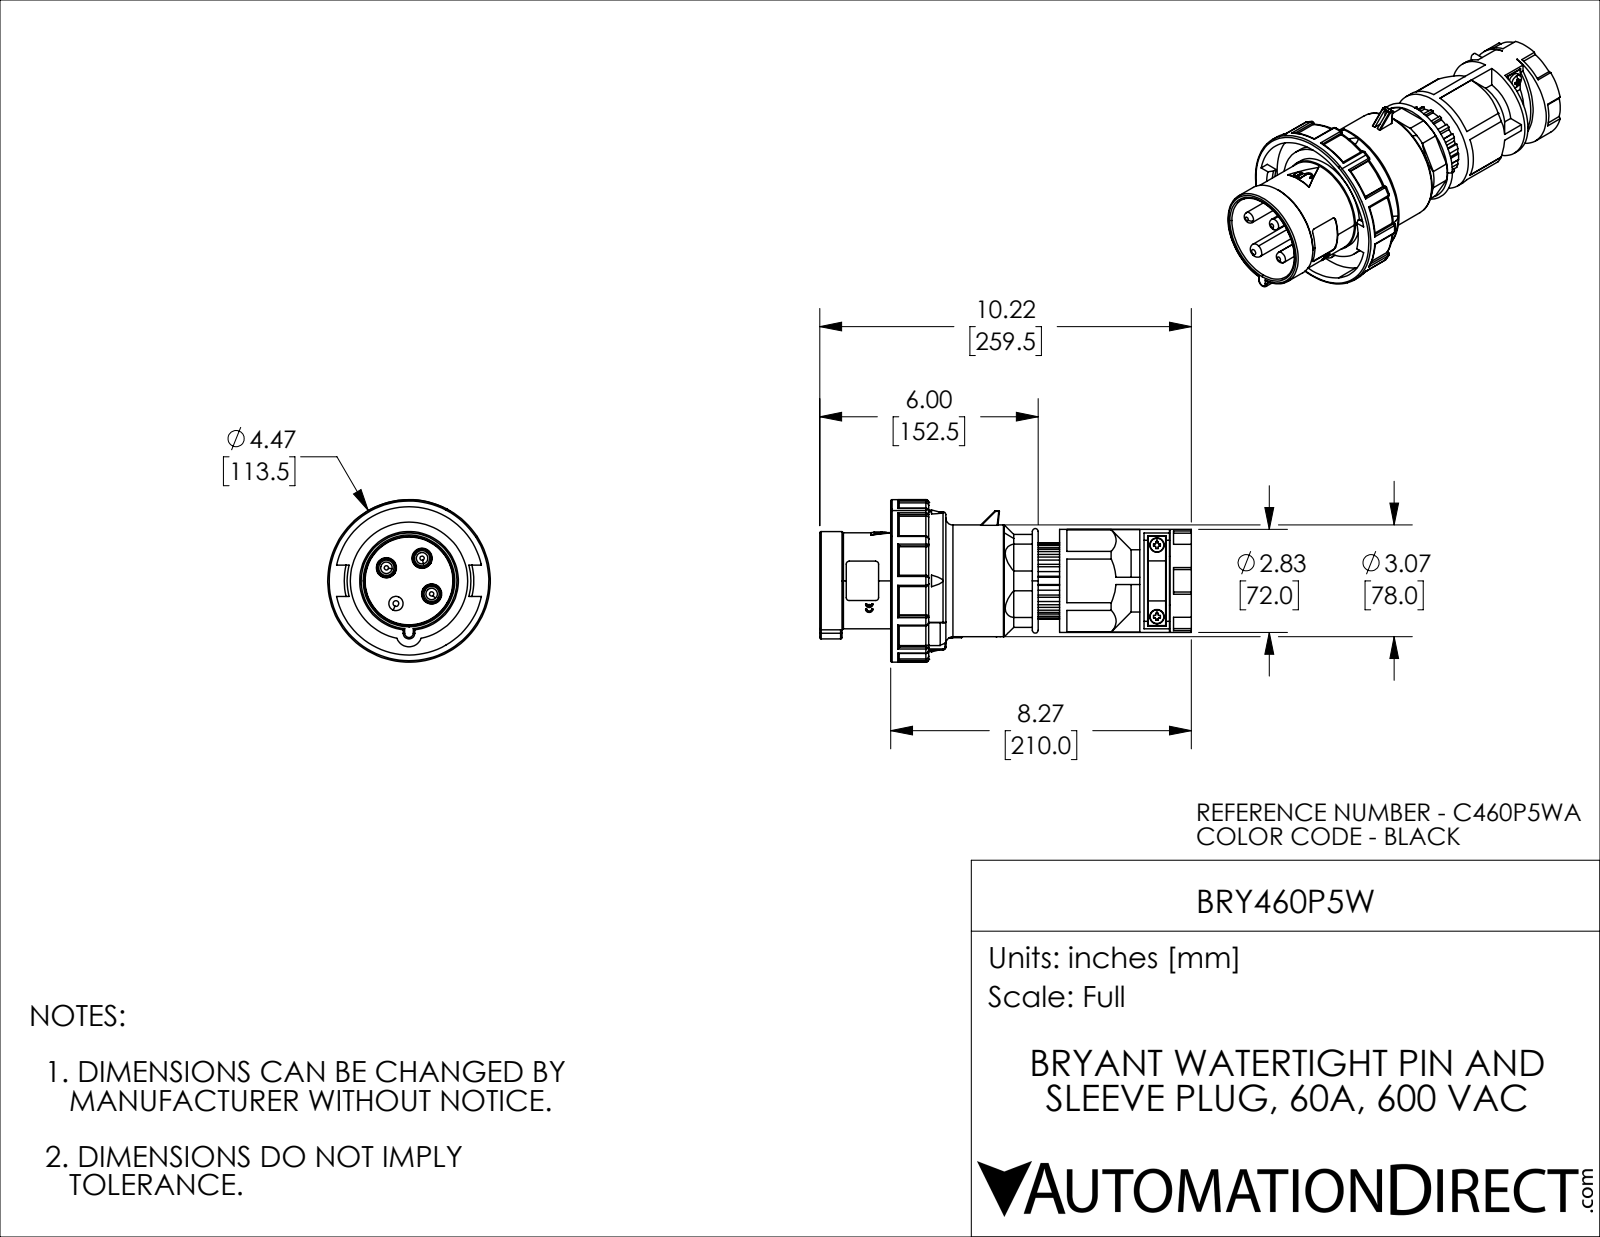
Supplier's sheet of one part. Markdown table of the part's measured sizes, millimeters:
| quantity | value |
| --- | --- |
| part name | BRY460P5W |
| STEP written by | SolidWorks 2021 (CONFIG_CONTROL_DESIGN) |
| units | millimeters |
| bodies | 1 solid, 1166 faces (494 planar, 374 cylindrical, 298 other) |
| overall size | 259.5 × 113.5 × 113.5 |
| volume | 753 097 mm³ |
| surface area | 145 798 mm² |
| round holes (diameter × count) | 2 × 2, 37 × 1, 62 × 1, 65.5 × 1, 103.5 × 1 |
| round bosses / shafts (diameter × count) | 8 × 3, 5 × 2, 113.5 × 1, 82 × 1, 78 × 1, 72 × 1, 68.9 × 1, 68.03 × 1 |
| partial cylindrical surfaces (radius × count) | 1 × 34, 0.5 × 23, 2 × 18, 34.5 × 6, 0.4 × 4, 3 × 3, 4 × 3, 1.2 × 2 |
| main face-to-face distances | 65, 15, 92, 3, 97, 18, 86, 26, 5, 15.5 |
